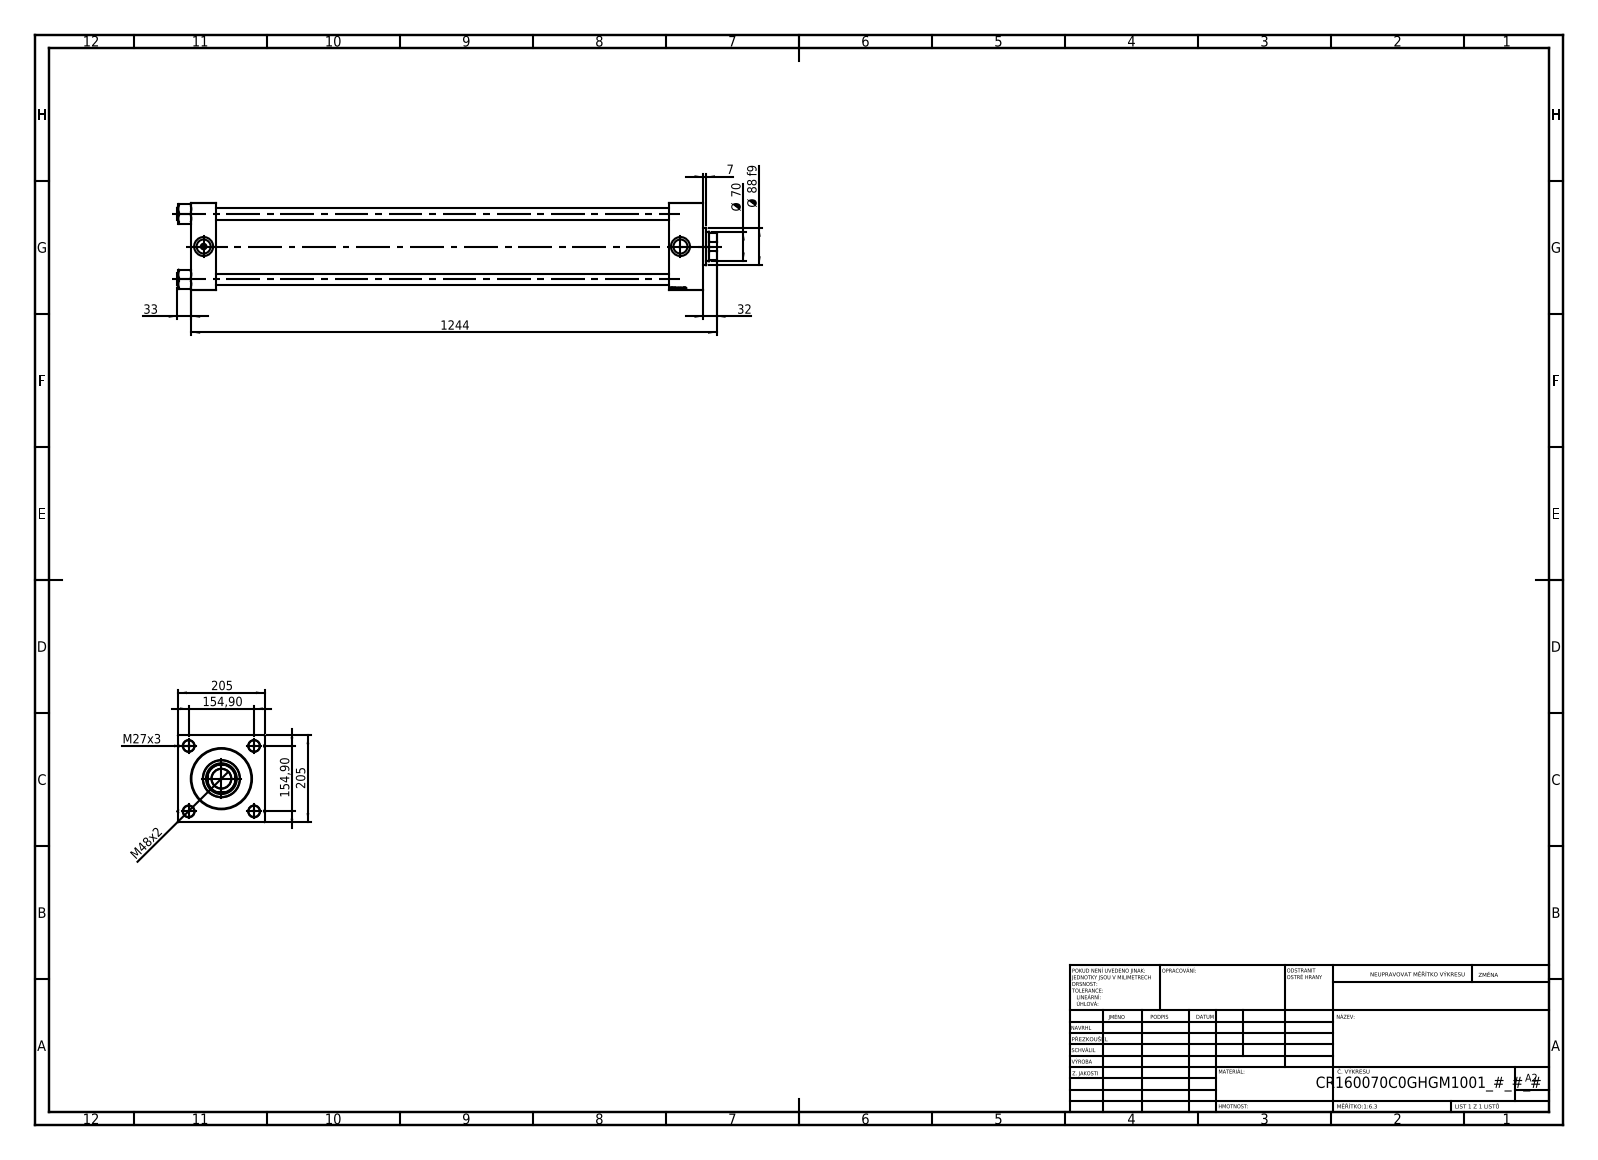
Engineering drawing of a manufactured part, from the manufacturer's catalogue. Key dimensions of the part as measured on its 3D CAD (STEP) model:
Part name (STEP PRODUCT): V215CR_C_TYCINKA; V215CR_C_Body; V215_VC_A; V215CR_VCP_C (+1 more)
STEP written by: SolidWorks 2019 (CONFIG_CONTROL_DESIGN)
Units: millimetres
Bodies: 11 solids, 1196 faces (574 planar, 86 cylindrical, 536 other)
Overall size (bounding box): 1277 × 208.14 × 205
Volume: 14 980 000 mm³ · Surface area: 2 248 000 mm²
Round holes (diameter × count): ⌀27 ×4, ⌀7 ×2, ⌀33.24 ×2, ⌀45 ×2, ⌀46.5 ×1, ⌀70 ×1, ⌀73 ×1, ⌀120 ×1, ⌀142 ×1, ⌀160 ×1
Round bosses / shafts (diameter × count): ⌀30 ×4, ⌀166 ×1, ⌀88 ×1
Partial cylindrical surfaces — rounded edges, fillets, slot ends (radius × count): R34 ×1
Main face-to-face distances: 205, 58, 1212, 1154, 1131, 1073, 81, 1183.3, 1125.3, 52.3
Hole centre spacings: 109.53, 154.9, 219.06, 1129
